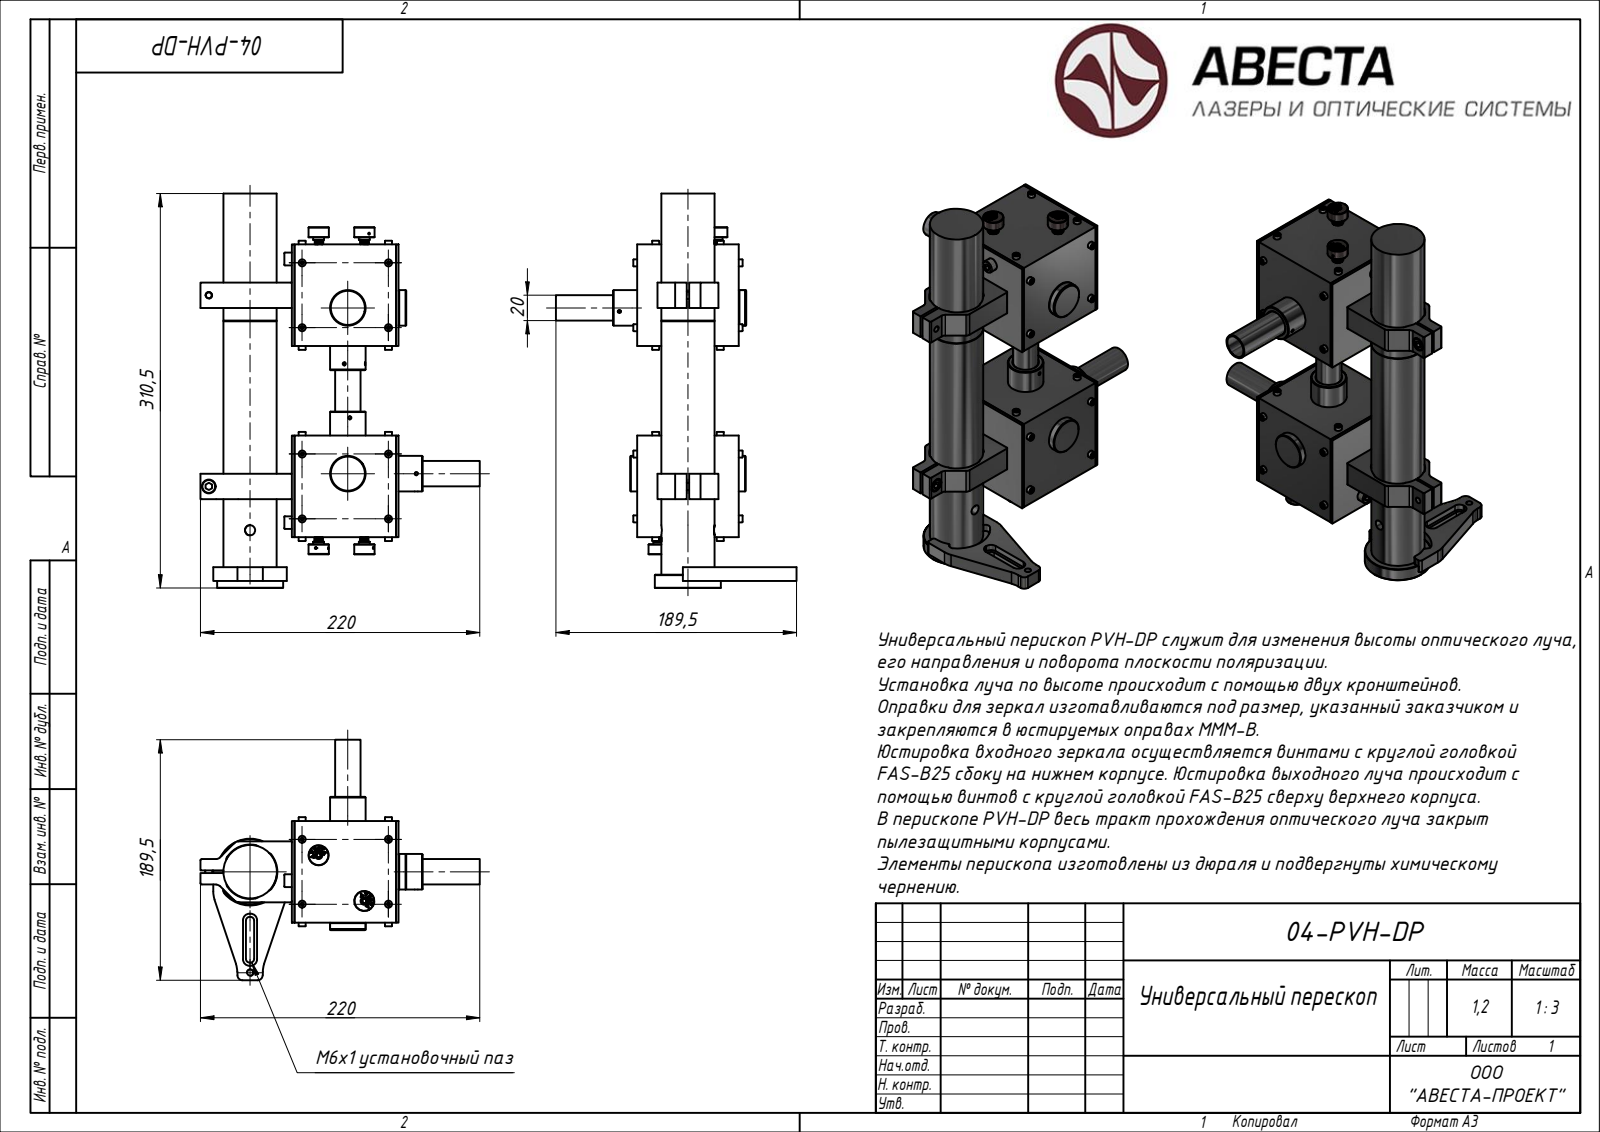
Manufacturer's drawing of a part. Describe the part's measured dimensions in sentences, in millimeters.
The part is named "Block 05; Block 04; Block 03; Block 02 (+1 more)". Its 3-D file was written by "ST-DEVELOPER v15 (AUTOMOTIVE_DESIGN)". It is 44 solids with 2791 faces: 0 planar, 0 cylindrical and 2791 other. Overall it measures 310.5 by 220 by 189.5 millimeters. Its volume is 26 915 cubic millimeters and its surface area 276 580 square millimeters.
